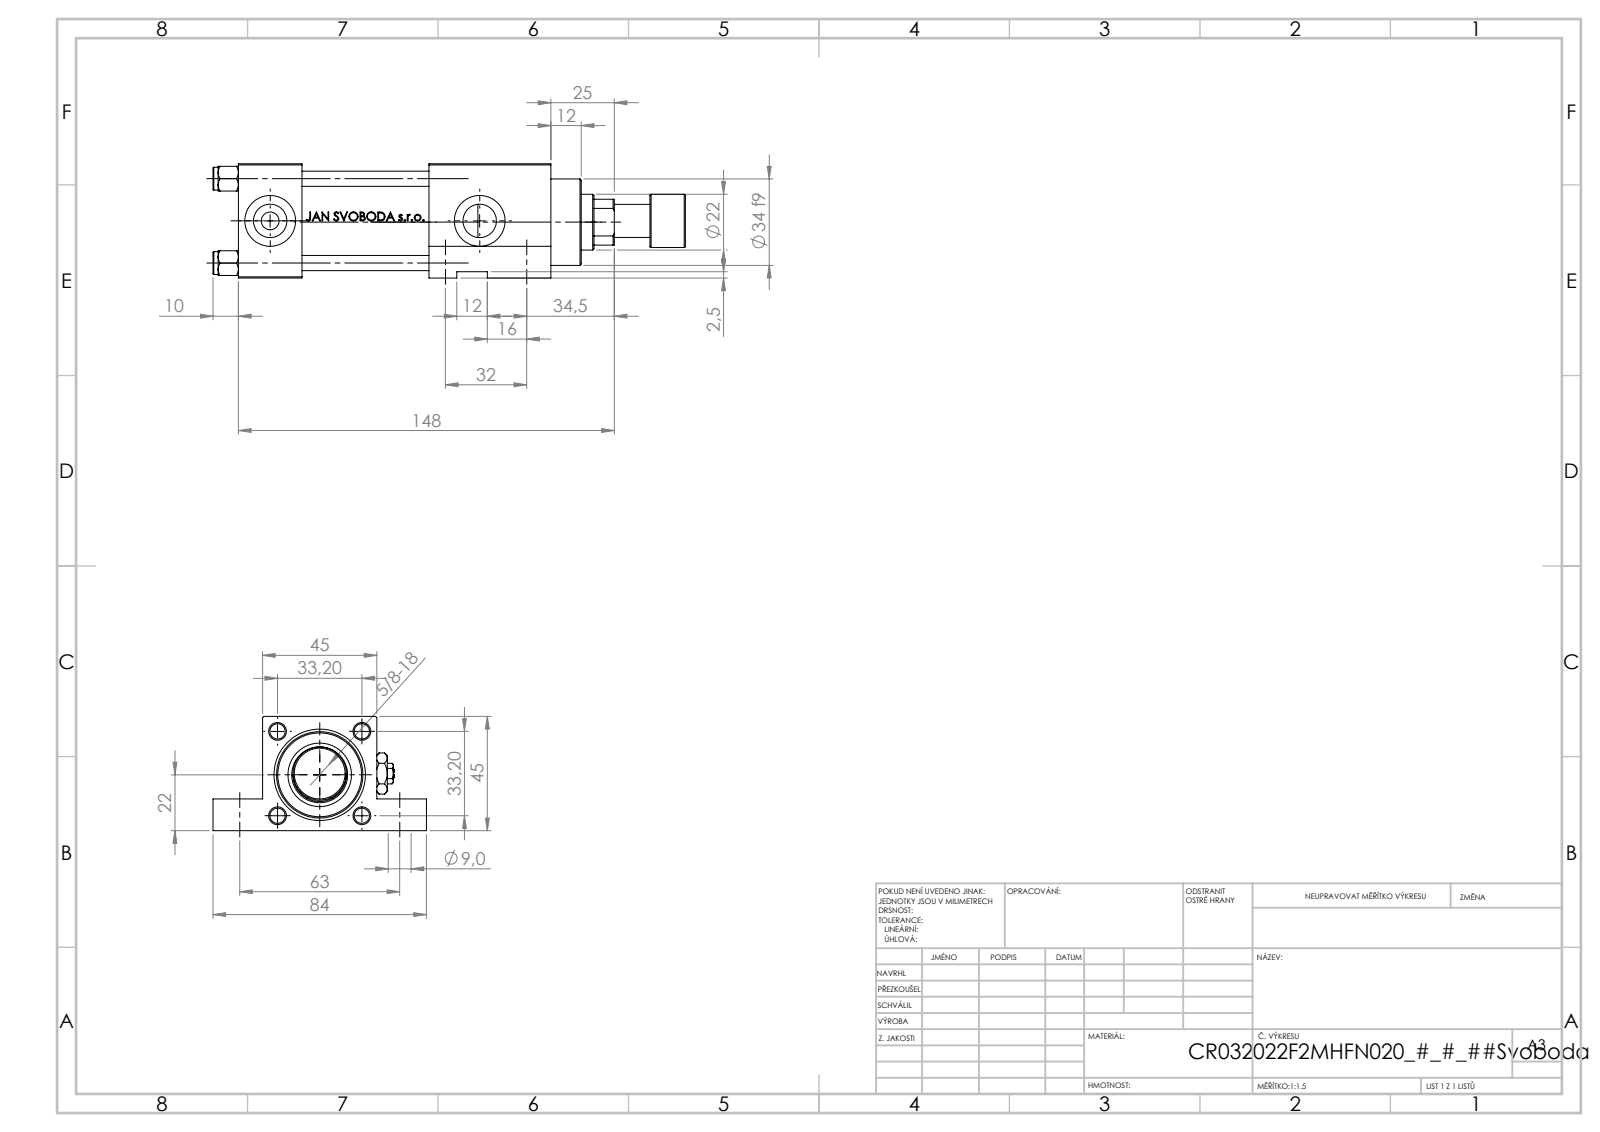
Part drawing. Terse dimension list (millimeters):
name: V215_VC_A; V215CR_F_Body; V215CR_F_TYCINKA; V215CR_VCP_F (+3 more)
written by: SolidWorks 2019 (CONFIG_CONTROL_DESIGN)
unit: mm
bodies: 13 solids, 1161 faces (461 planar, 134 cylindrical, 566 other)
size: 186 × 84 × 45
volume: 233 761 mm³; area: 80 103 mm²
holes: 4× ⌀6, 4× ⌀9, 2× ⌀7, 2× ⌀13.16, 2× ⌀20, 1× ⌀10.5, 1× ⌀13, 1× ⌀22, 1× ⌀24, 1× ⌀25, 1× ⌀32, 1× ⌀33
bosses: 4× ⌀9, 1× ⌀38, 1× ⌀34, 1× ⌀21, 1× ⌀13
rounds: 1× R10.5
face distances: 45, 25, 50, 98, 123, 75, 12.5, 32.5, 48, 10
hole spacings: 33.2, 23.13, 23.83, 32, 46.95, 63, 70.66, 82.5
